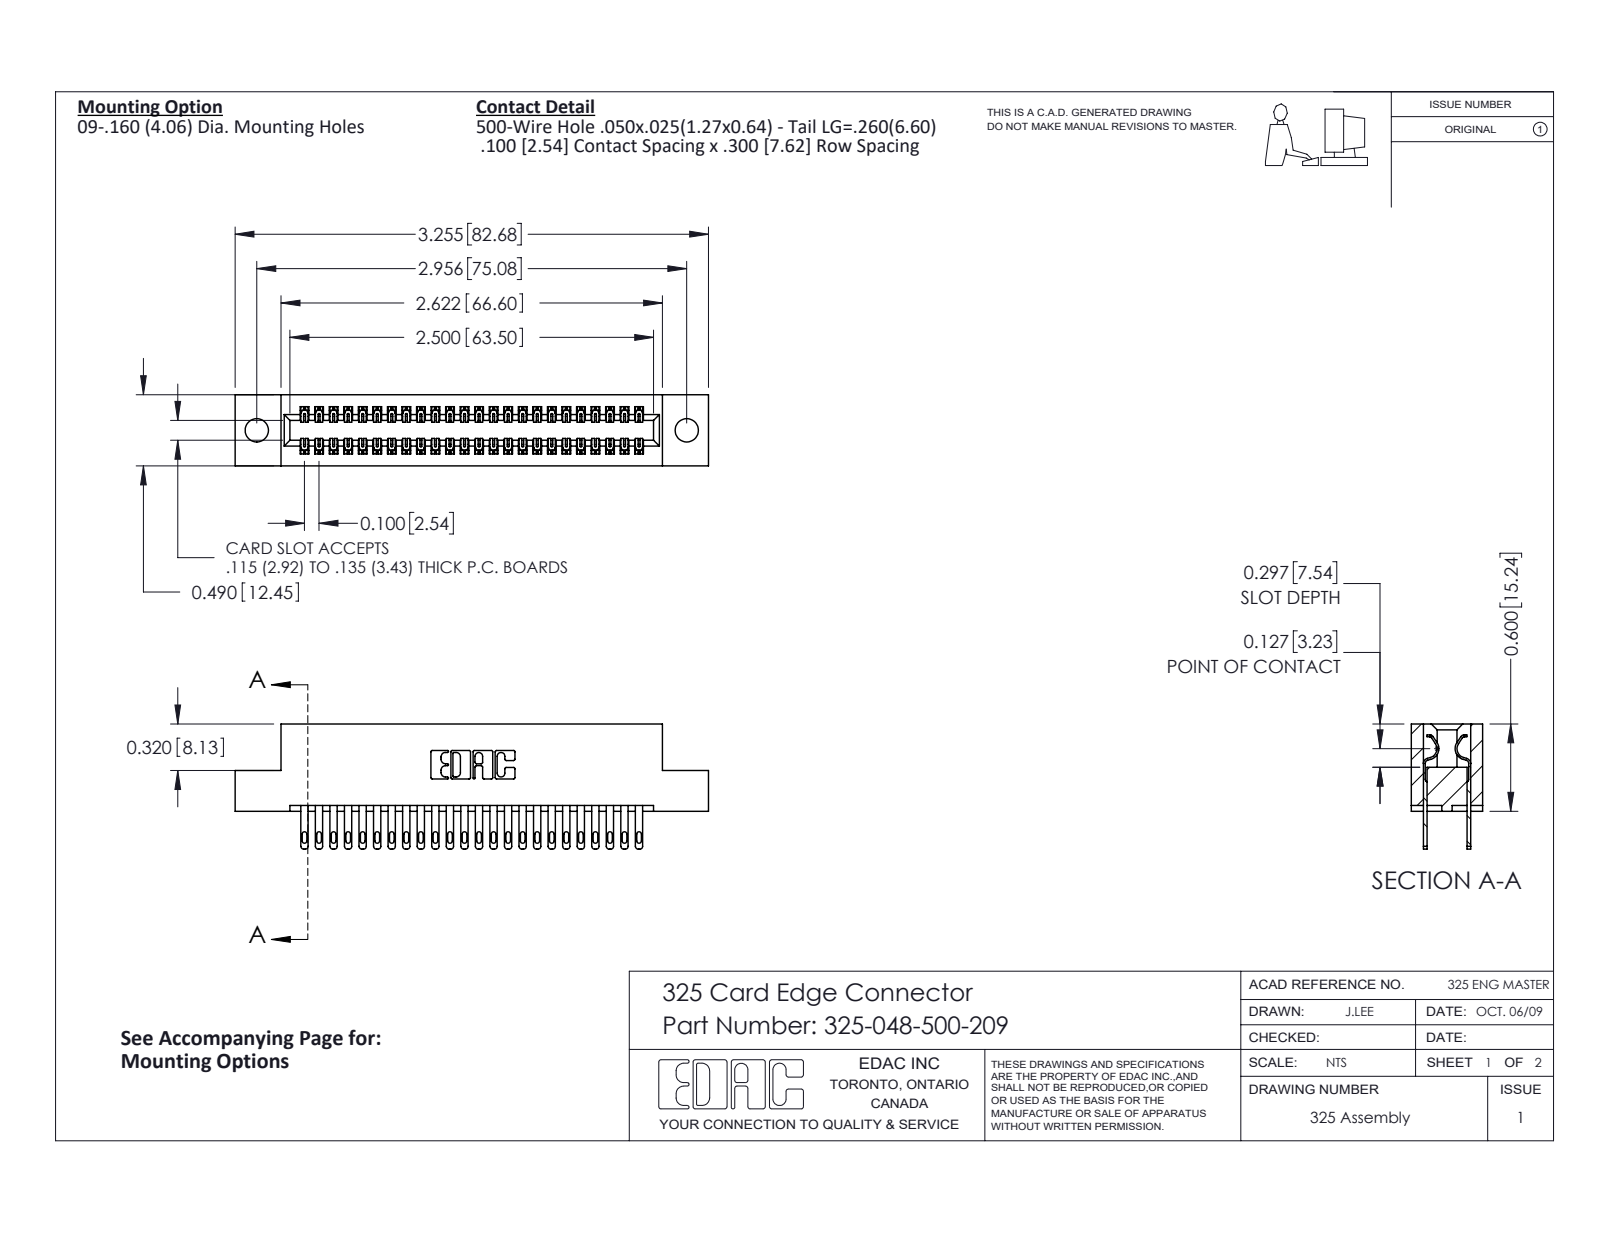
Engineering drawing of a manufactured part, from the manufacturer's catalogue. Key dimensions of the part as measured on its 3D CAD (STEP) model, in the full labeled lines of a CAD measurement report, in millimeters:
Part name (STEP PRODUCT): 325 Part_.160 TH; 325-048-500-209; 325-292-001_325-293-100
STEP written by: SolidWorks 2016 (CONFIG_CONTROL_DESIGN)
Units: millimetres
Bodies: 49 solids, 2418 faces (1510 planar, 908 cylindrical, 0 other)
Overall size (bounding box): 82.7 × 21.8 × 12.4
Volume: 10 400 mm³ · Surface area: 12 620 mm²
Round holes (diameter × count): ⌀4.1 ×2
Partial cylindrical surfaces — rounded edges, fillets, slot ends (radius × count): R0.2 ×72, R0.4 ×48, R0.5 ×48, R0.3 ×22, R0.2 ×6, R0.8 ×6, R0.7 ×3, R0.4 ×2
Main face-to-face distances: 2.1, 10.3, 7.6, 2.7, 9.7, 0.6, 12.4, 8.3, 7, 1
Hole centre spacings: 75.1
